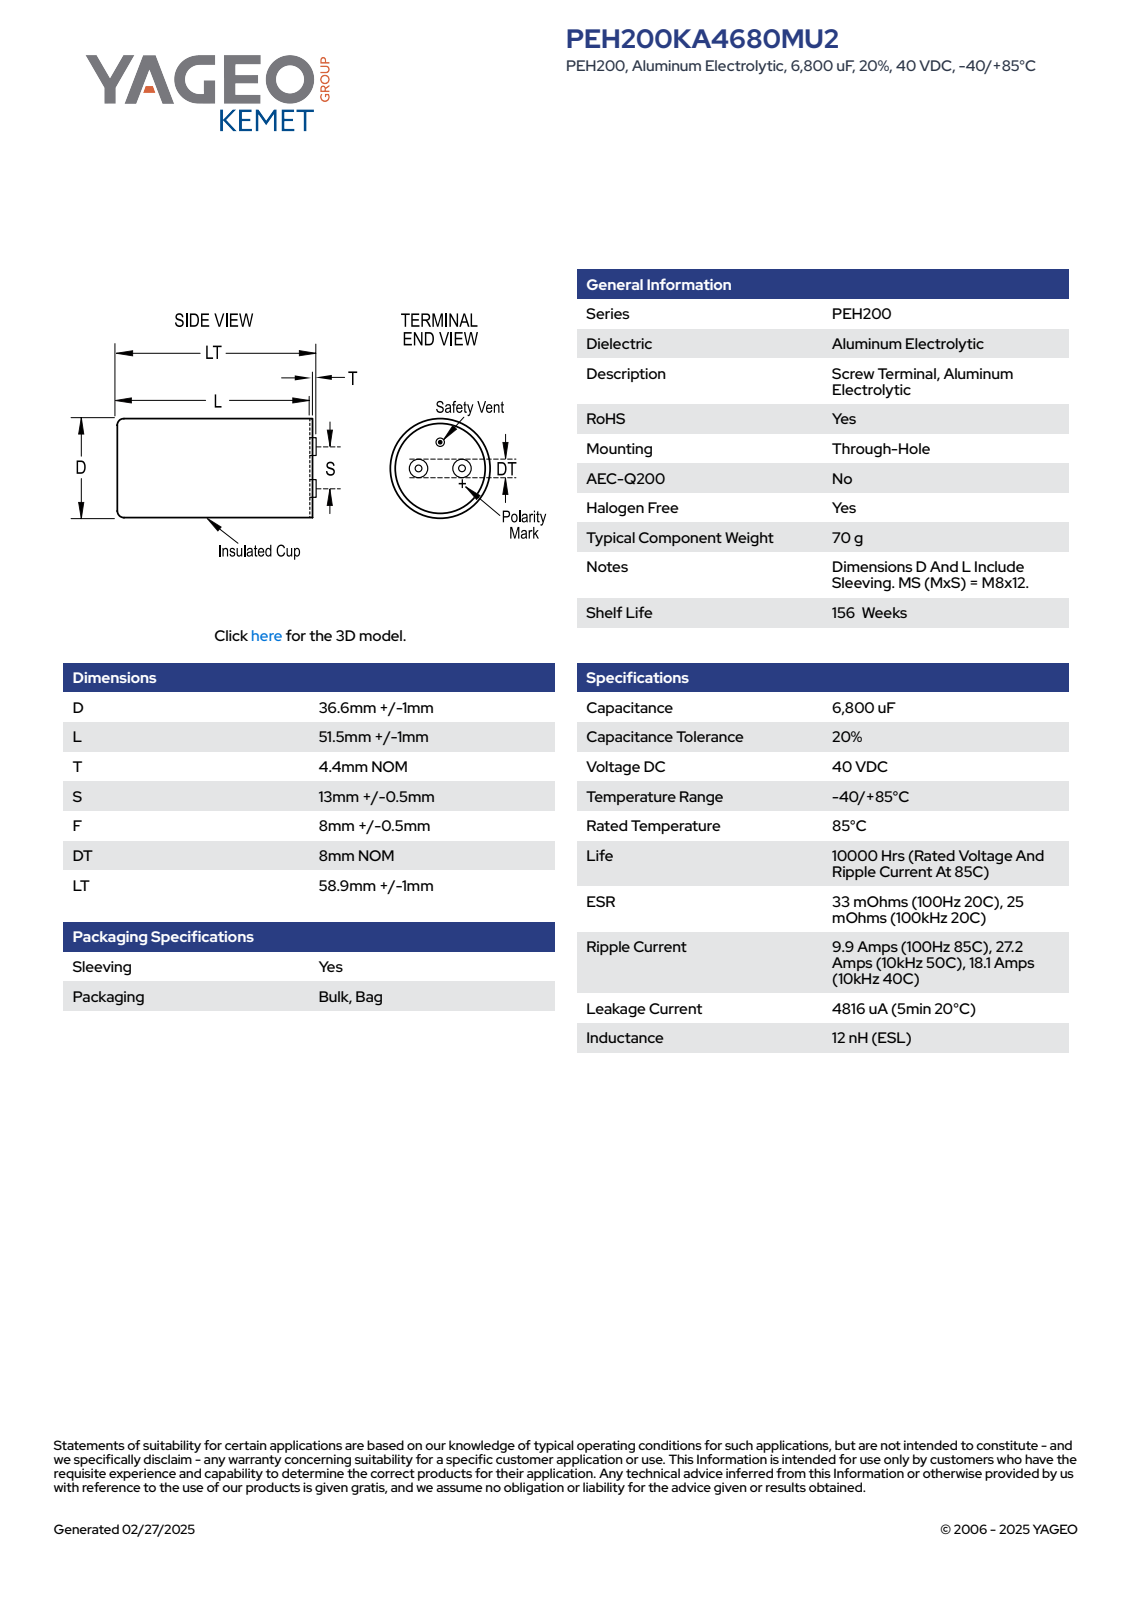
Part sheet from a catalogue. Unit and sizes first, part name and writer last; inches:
Units: inches
Overall size (bounding box): 2.358 × 1.48 × 1.48
Round holes (diameter × count): ⌀0.197 ×2, ⌀1.402 ×1
Round bosses / shafts (diameter × count): ⌀0.315 ×2, ⌀1.48 ×1
Partial cylindrical surfaces — rounded edges, fillets, slot ends (radius × count): R0.74 ×1
Main face-to-face distances: 2.067, 0.118, 2.185, 0.173, 0.291, 2.358, 0.689, 0.516, 0.398, 1.669
Hole centre spacings: 0.256, 0.512
Volume: 3.582 in³ · Surface area: 14.93 in²
Bodies: 3 solids, 77 faces (30 planar, 15 cylindrical, 32 other)
Part name (STEP PRODUCT): Can_Round_1; Round_Terminal; CARC_D37.6L52.5S13T4.4
STEP written by: SolidWorks 2014 (AUTOMOTIVE_DESIGN)
